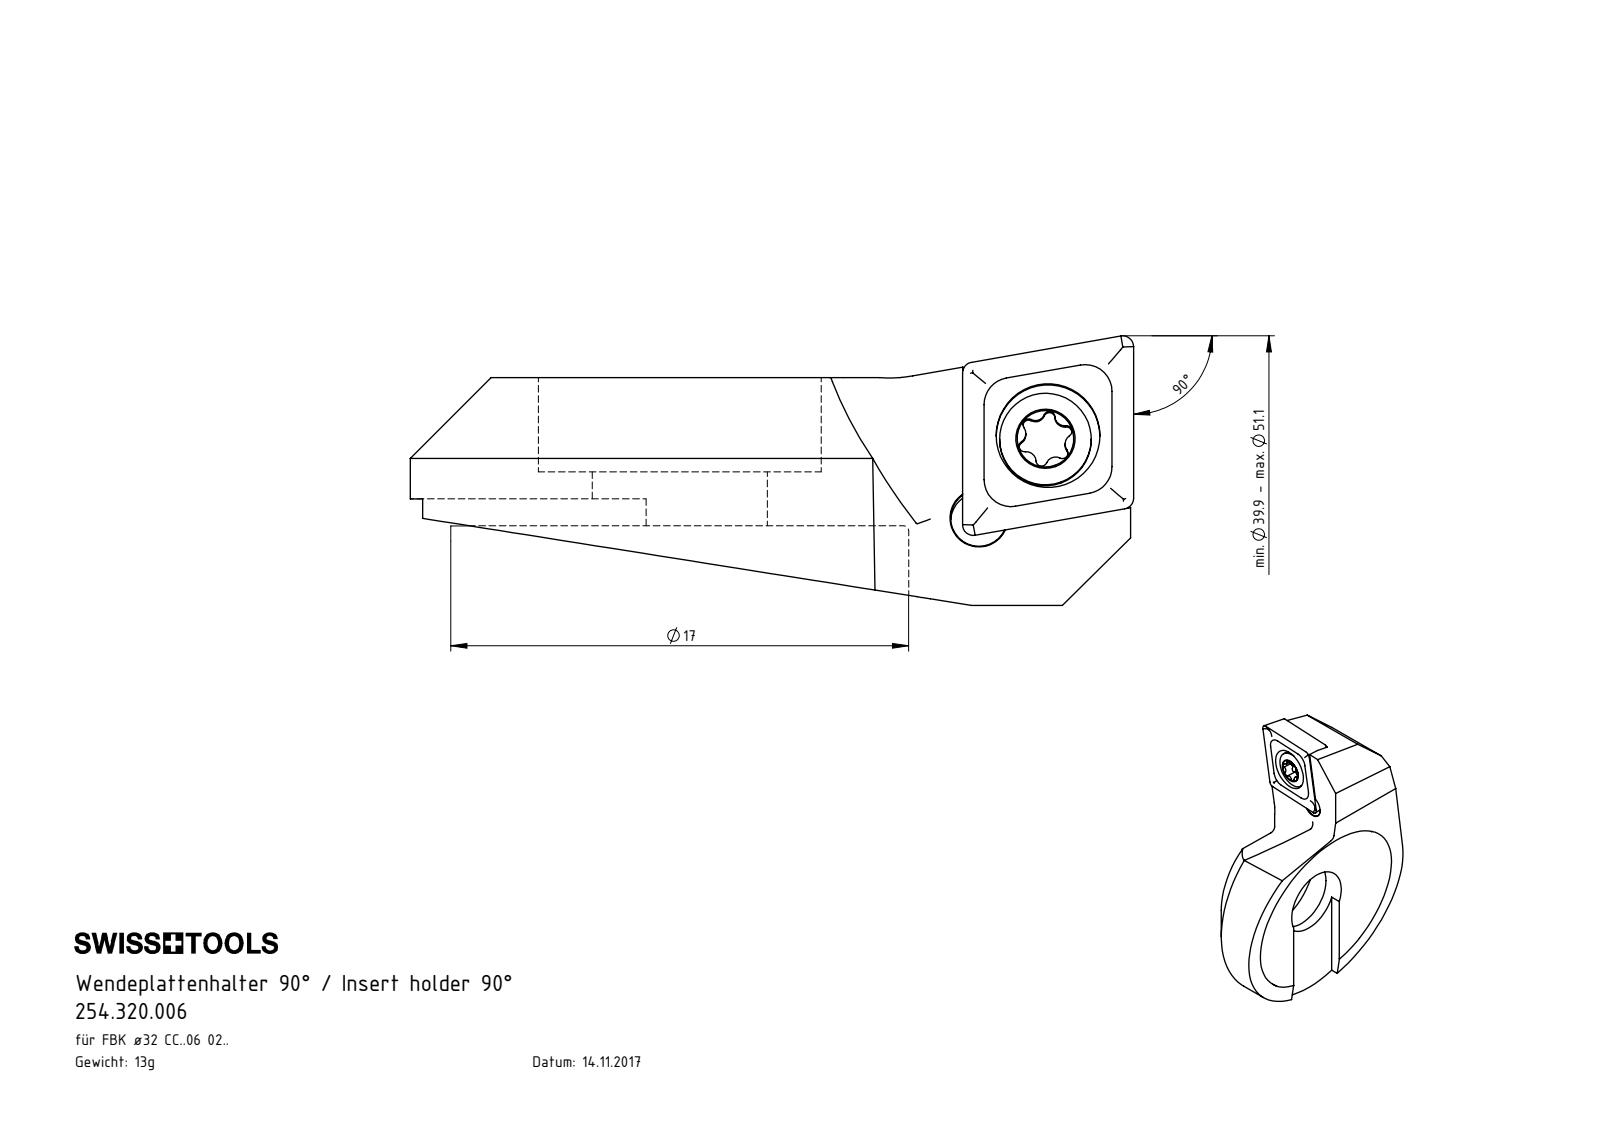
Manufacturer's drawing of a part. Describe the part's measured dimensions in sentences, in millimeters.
The part is named "CCMT060204; F32-WCA.001.007_C_fertigbearbeitet; WCA-ER2.001.006_A; F32-WCA.001.007_C (+1 more)". Its 3-D file was written by "SolidWorks 2017 (AUTOMOTIVE_DESIGN)". It is 3 solids with 133 faces: 38 planar, 42 cylindrical and 53 other. Overall it measures 26.85 by 20 by 10 millimeters. Its volume is 1 558 cubic millimeters and its surface area 1 543 square millimeters. Round holes: 1 of diameter 2.05, 1 of diameter 2.1, 1 of diameter 2.8, 1 of diameter 3.85, 1 of diameter 6.5, 1 of diameter 10.5. Round bosses or shafts: 1 of diameter 3.4, 1 of diameter 2.5. Partial cylindrical surfaces (rounded edges, fillets, slot ends): 6 of radius 0.21, 5 of radius 0.36, 2 of radius 0.5, 1 of radius 0.36, 1 of radius 5, 1 of radius 8.5, 1 of radius 10, 1 of radius 15. The main face-to-face distances are 1, 5.5, 3.5, 2, 4.5, 2.28, 8.45, 4.95, 3.95, 2.95. The hole center spacings are 3.84, 3.99.
